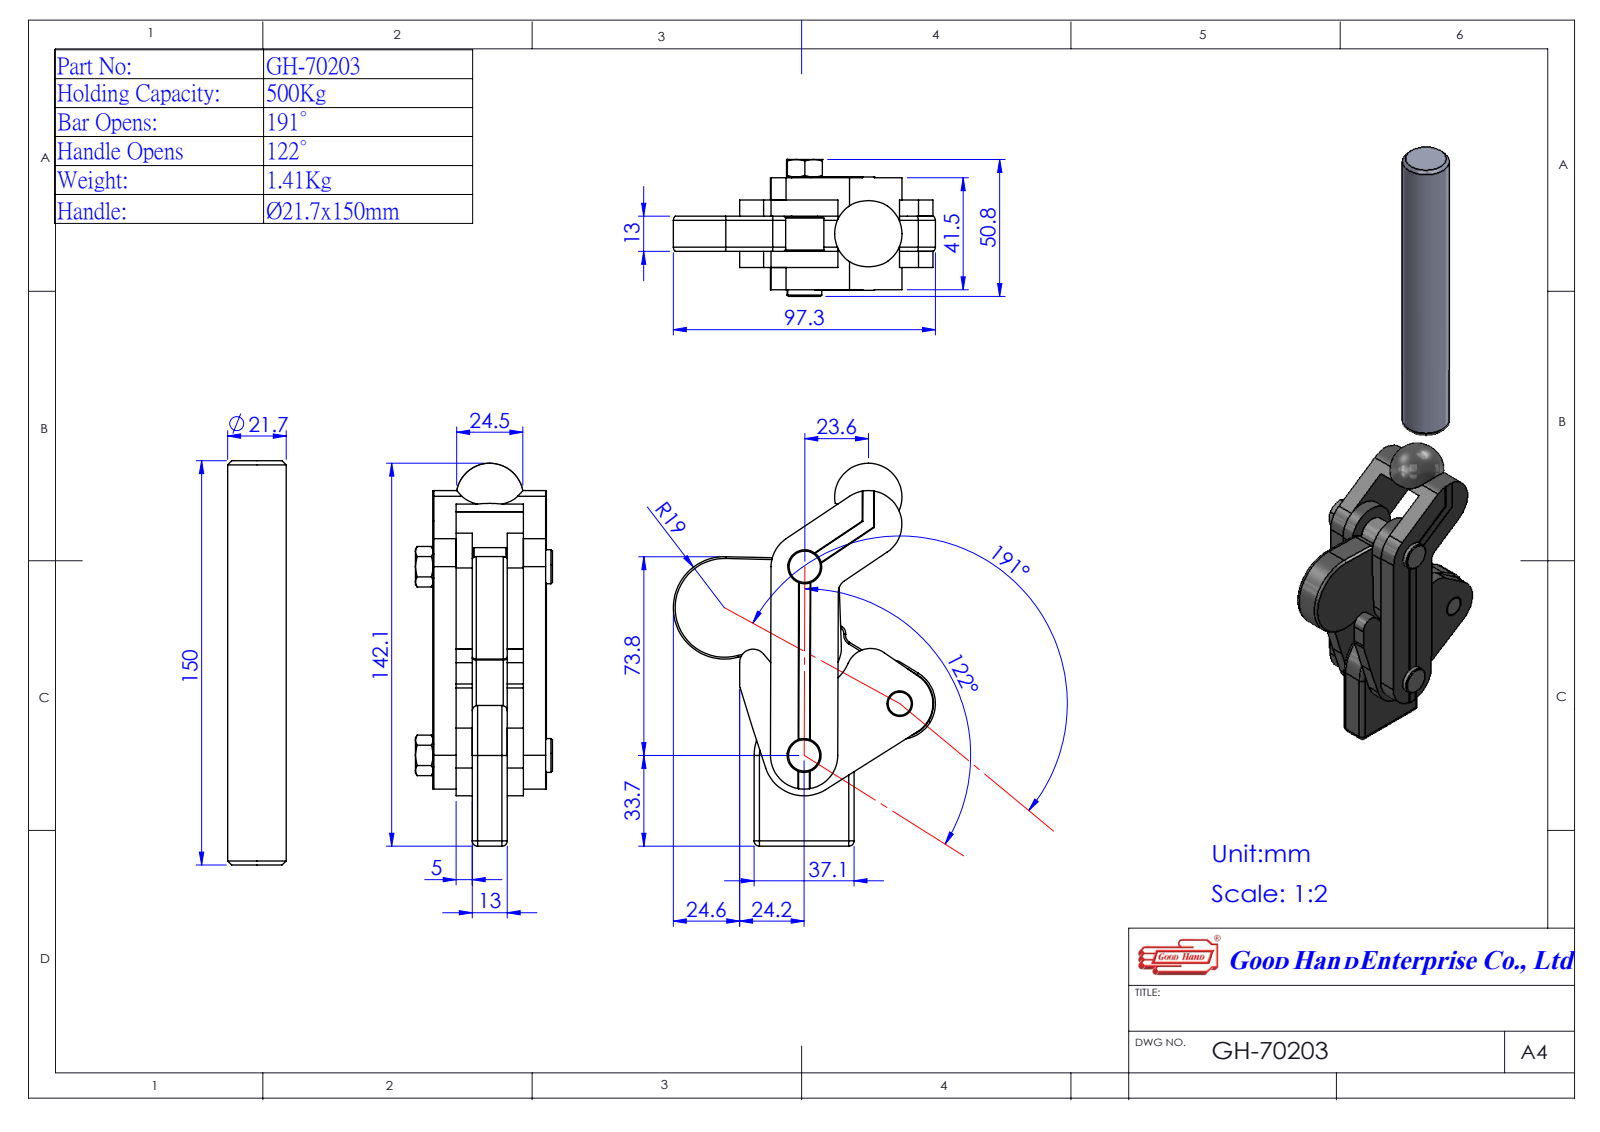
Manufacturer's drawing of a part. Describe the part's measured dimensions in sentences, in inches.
The part is named "3700208-1^GH-70203(簡化); 4702D152; 3700229-1^GH-70203(簡化); Group4^GH-70203(簡化) (+3 more)". Its 3-D file was written by "SolidWorks 2016 (AUTOMOTIVE_DESIGN)". It is 6 solids with 254 faces: 120 planar, 104 cylindrical and 30 other. Overall it measures 11.545 by 3.831 by 2 inches. Its volume is 11.45 cubic inches and its surface area 118 square inches. Round holes: 4 of diameter 0.374, 1 of diameter 0.665. Round bosses or shafts: 4 of diameter 0.375, 2 of diameter 0.496, 1 of diameter 0.854, 1 of diameter 0.559. Partial cylindrical surfaces (rounded edges, fillets, slot ends): 12 of radius 0.059, 4 of radius 0.118, 4 of radius 0.197, 4 of radius 0.492, 2 of radius 0.591, 1 of radius 0.187, 1 of radius 0.354, 1 of radius 0.394. The main face-to-face distances are 0.748, 0.236, 0.512, 0.984, 0.325, 0.561, 1.073, 1.309, 1.634, 0.985. The hole center spacings are 1.181, 1.575, 1.576, 1.589, 2.434, 2.756.
